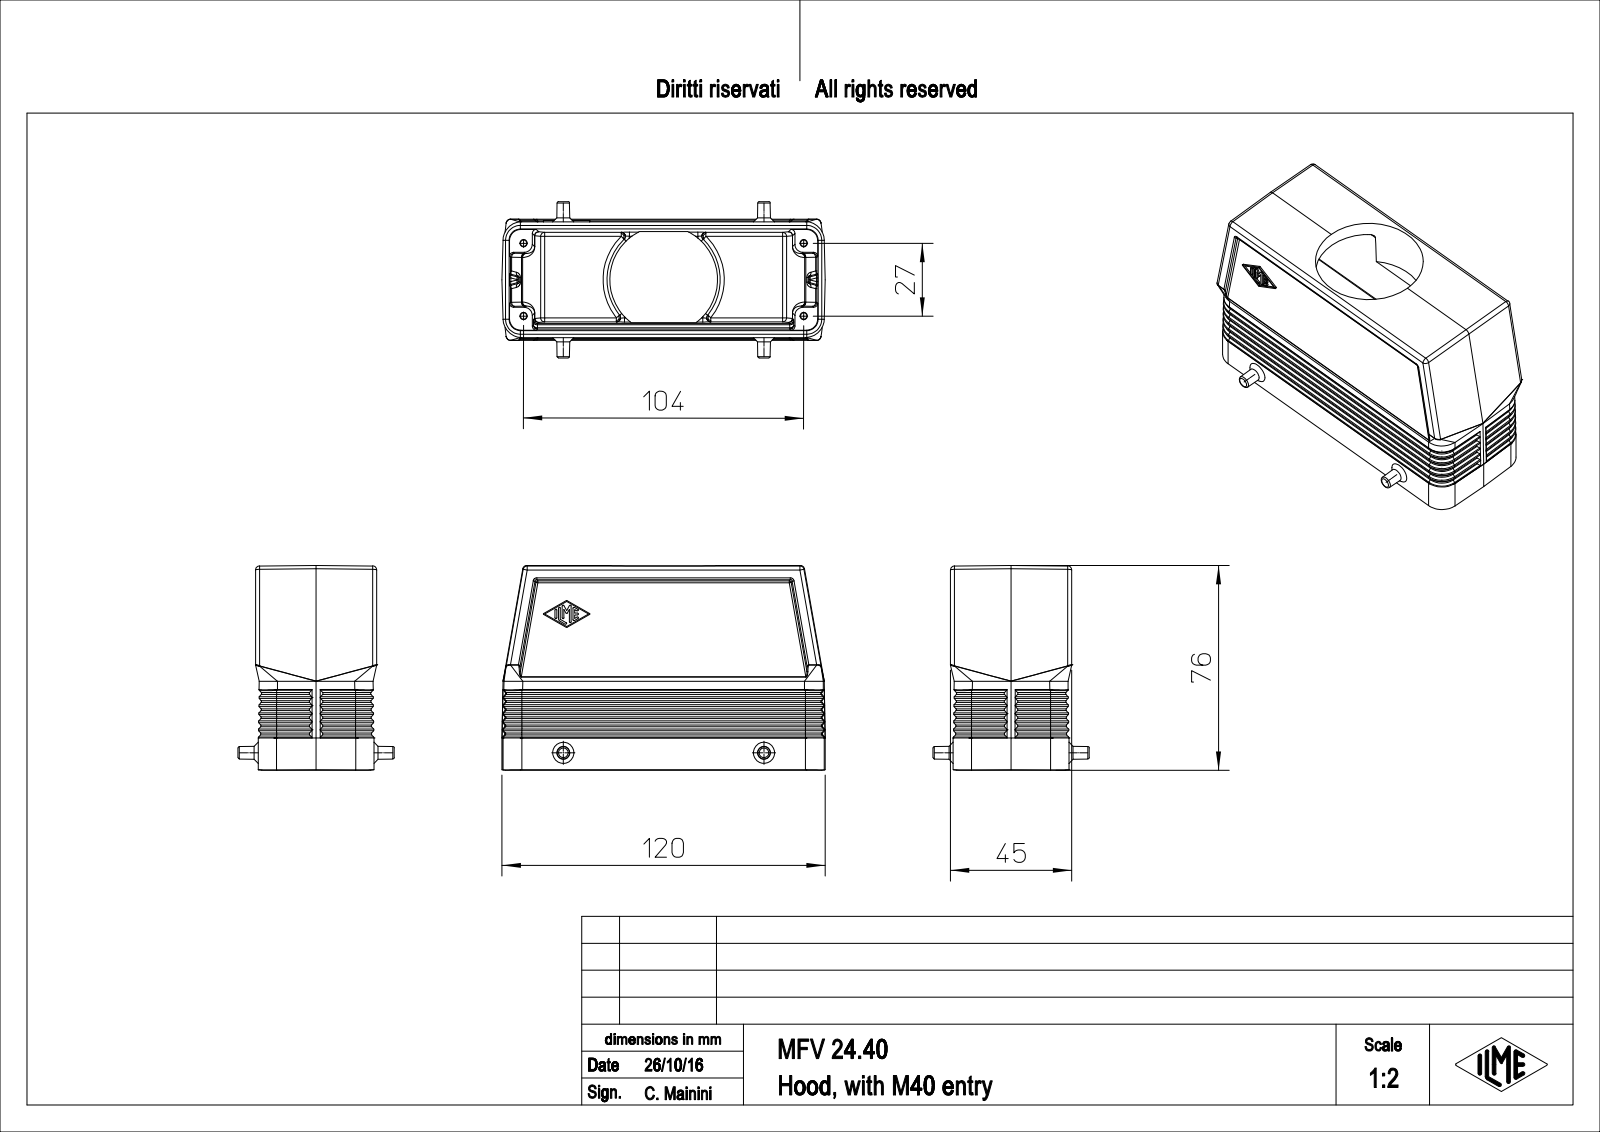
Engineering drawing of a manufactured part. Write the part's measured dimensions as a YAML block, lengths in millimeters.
part_name: "MFV_24.40"
step_written_by: "PTC Creo Elements/Direct Modeling 19.0E 27-Jun-2016 (C) Parametric Technology GmbH (AUTOMOTIVE_DESIGN)"
units: millimeters
bodies: {solids: 1, faces: 478, planar: 210, cylindrical: 132, other: 136}
overall_size: [120, 76, 58]
volume: 102351
surface_area: 53384
round_holes:
  - {diameter: 2.75, count: 4}
  - {diameter: 40, count: 1}
round_bosses_or_shafts:
  - {diameter: 4.59, count: 2}
partial_cylinders:
  - {radius: 0.5, count: 78}
  - {radius: 1.5, count: 10}
  - {radius: 7, count: 8}
  - {radius: 3, count: 4}
  - {radius: 4.2, count: 4}
  - {radius: 21, count: 1}
face_to_face_distances: [43, 2.01, 2, 4, 44, 1, 8.45, 6, 6.01, 4.01]
hole_center_spacings: [53.72, 27, 104, 107.45]
